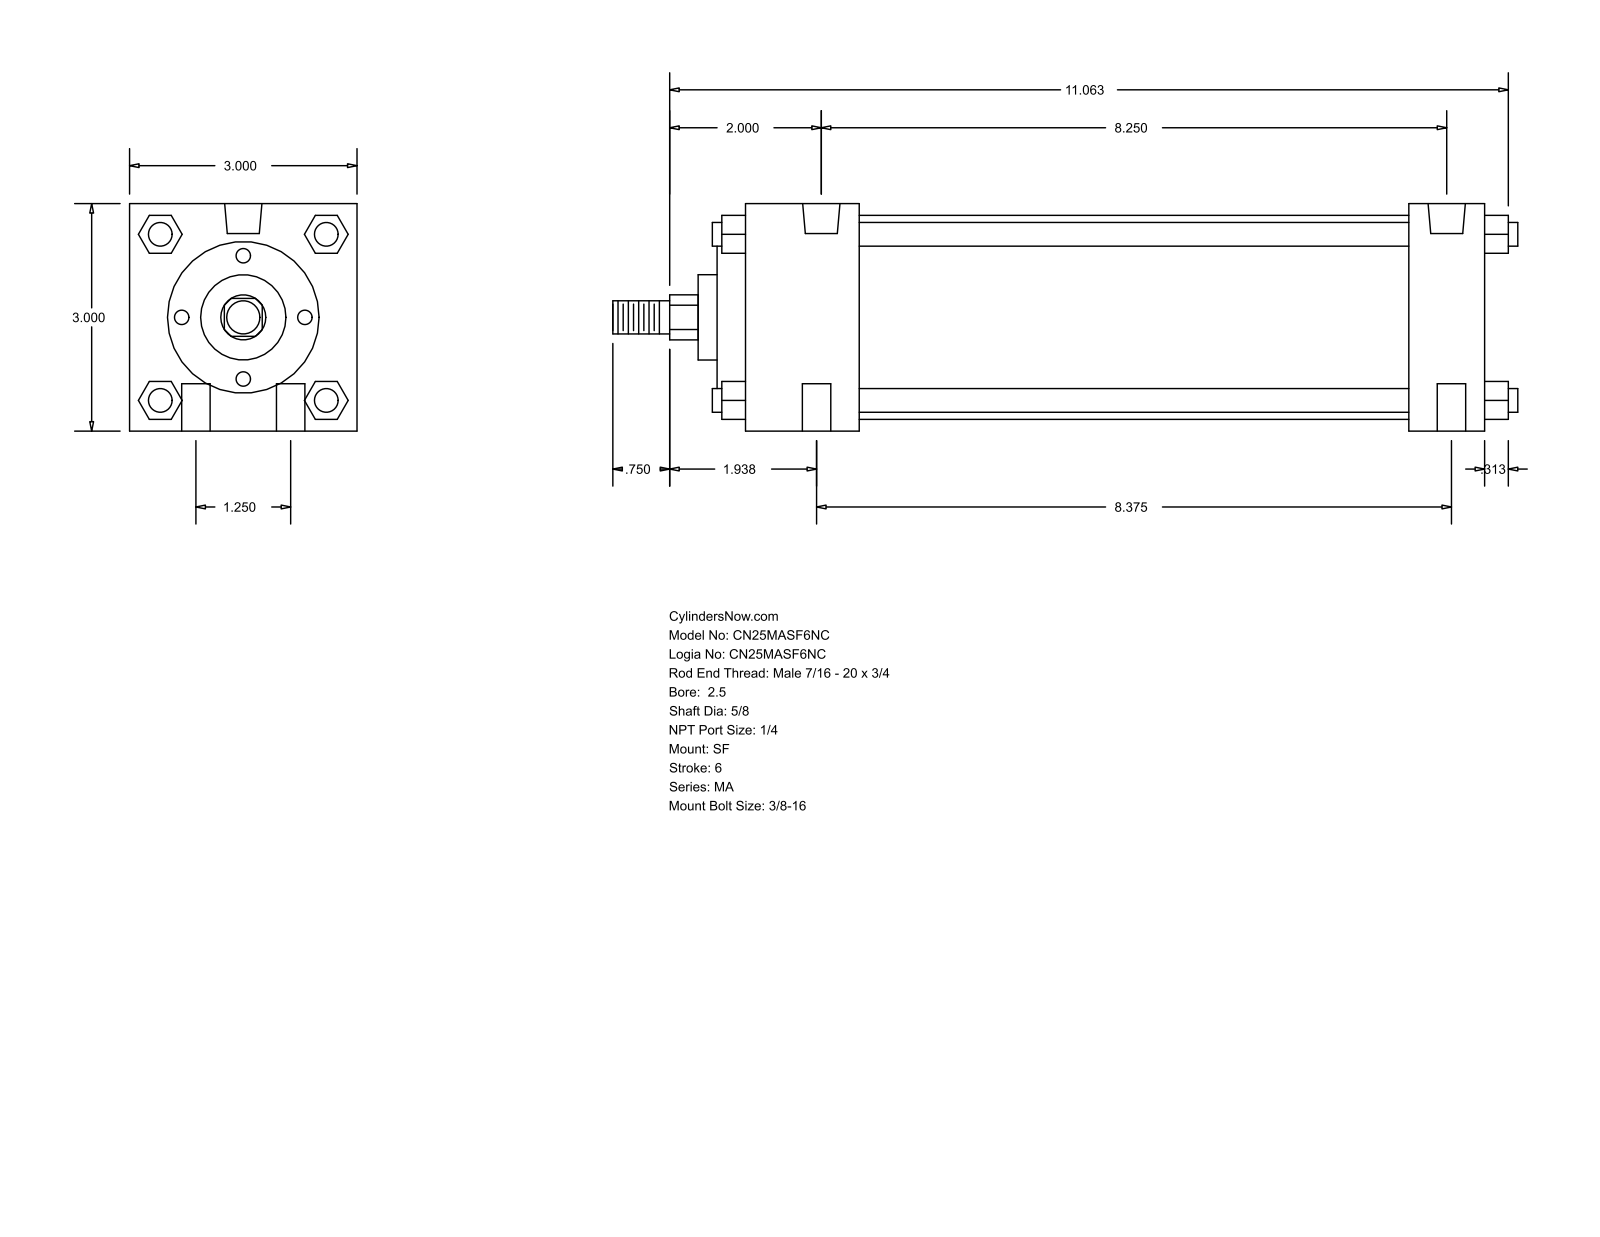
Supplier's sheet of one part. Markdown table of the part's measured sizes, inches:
| quantity | value |
| --- | --- |
| part name | MA_SF__0250_0.625 |
| STEP written by | GSSL Pune (CONFIG_CONTROL_DESIGN) |
| units | inches |
| bodies | 0 solids, 126 faces (95 planar, 31 cylindrical, 0 other) |
| overall size | 11.937 × 3 × 3 |
| round holes (diameter × count) | 0.375 × 4, 0.313 × 2, 0.492 × 2 |
| round bosses / shafts (diameter × count) | 0.313 × 4, 2.69 × 1, 2 × 1, 1.125 × 1, 0.625 × 1, 0.437 × 1 |
| partial cylindrical surfaces (radius × count) | 0.297 × 1 |
| main face-to-face distances | 3, 9.75, 1, 8.75, 1.5, 7.25, 8.25, 0.5, 0.375, 1.875 |
| hole center spacings | 0.628, 8.336, 1.25, 8.25, 8.375, 8.468 |
